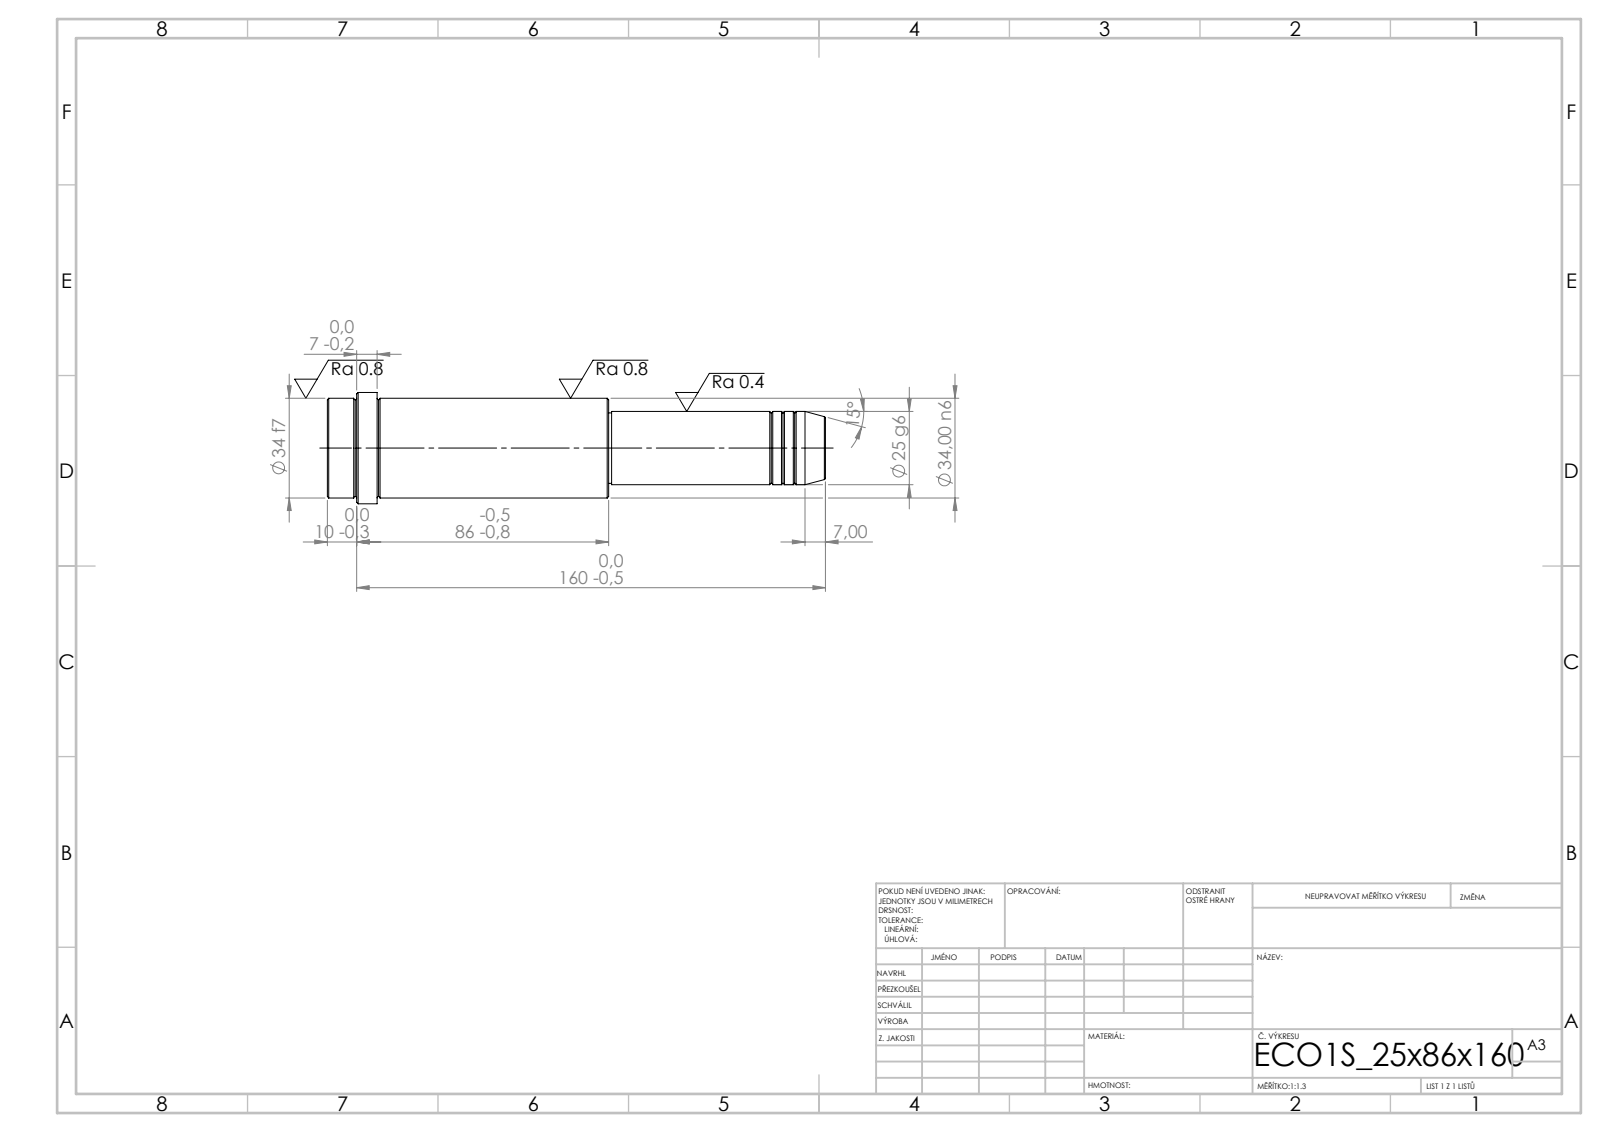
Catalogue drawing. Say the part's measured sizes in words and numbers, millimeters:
Its 3-D file was written by "SolidWorks 2019 (CONFIG_CONTROL_DESIGN)". It is 1 solid with 52 faces: 6 planar, 16 cylindrical and 30 other. Overall it measures 170 by 38 by 38 millimeters. Its volume is 124 323 cubic millimeters and its surface area 18 471 square millimeters. Round bosses or shafts: 1 of diameter 38, 1 of diameter 34, 1 of diameter 25, 1 of diameter 24. The main face-to-face distances are 96, 74, 170, 153, 79, 17, 160, 86, 7, 10.
